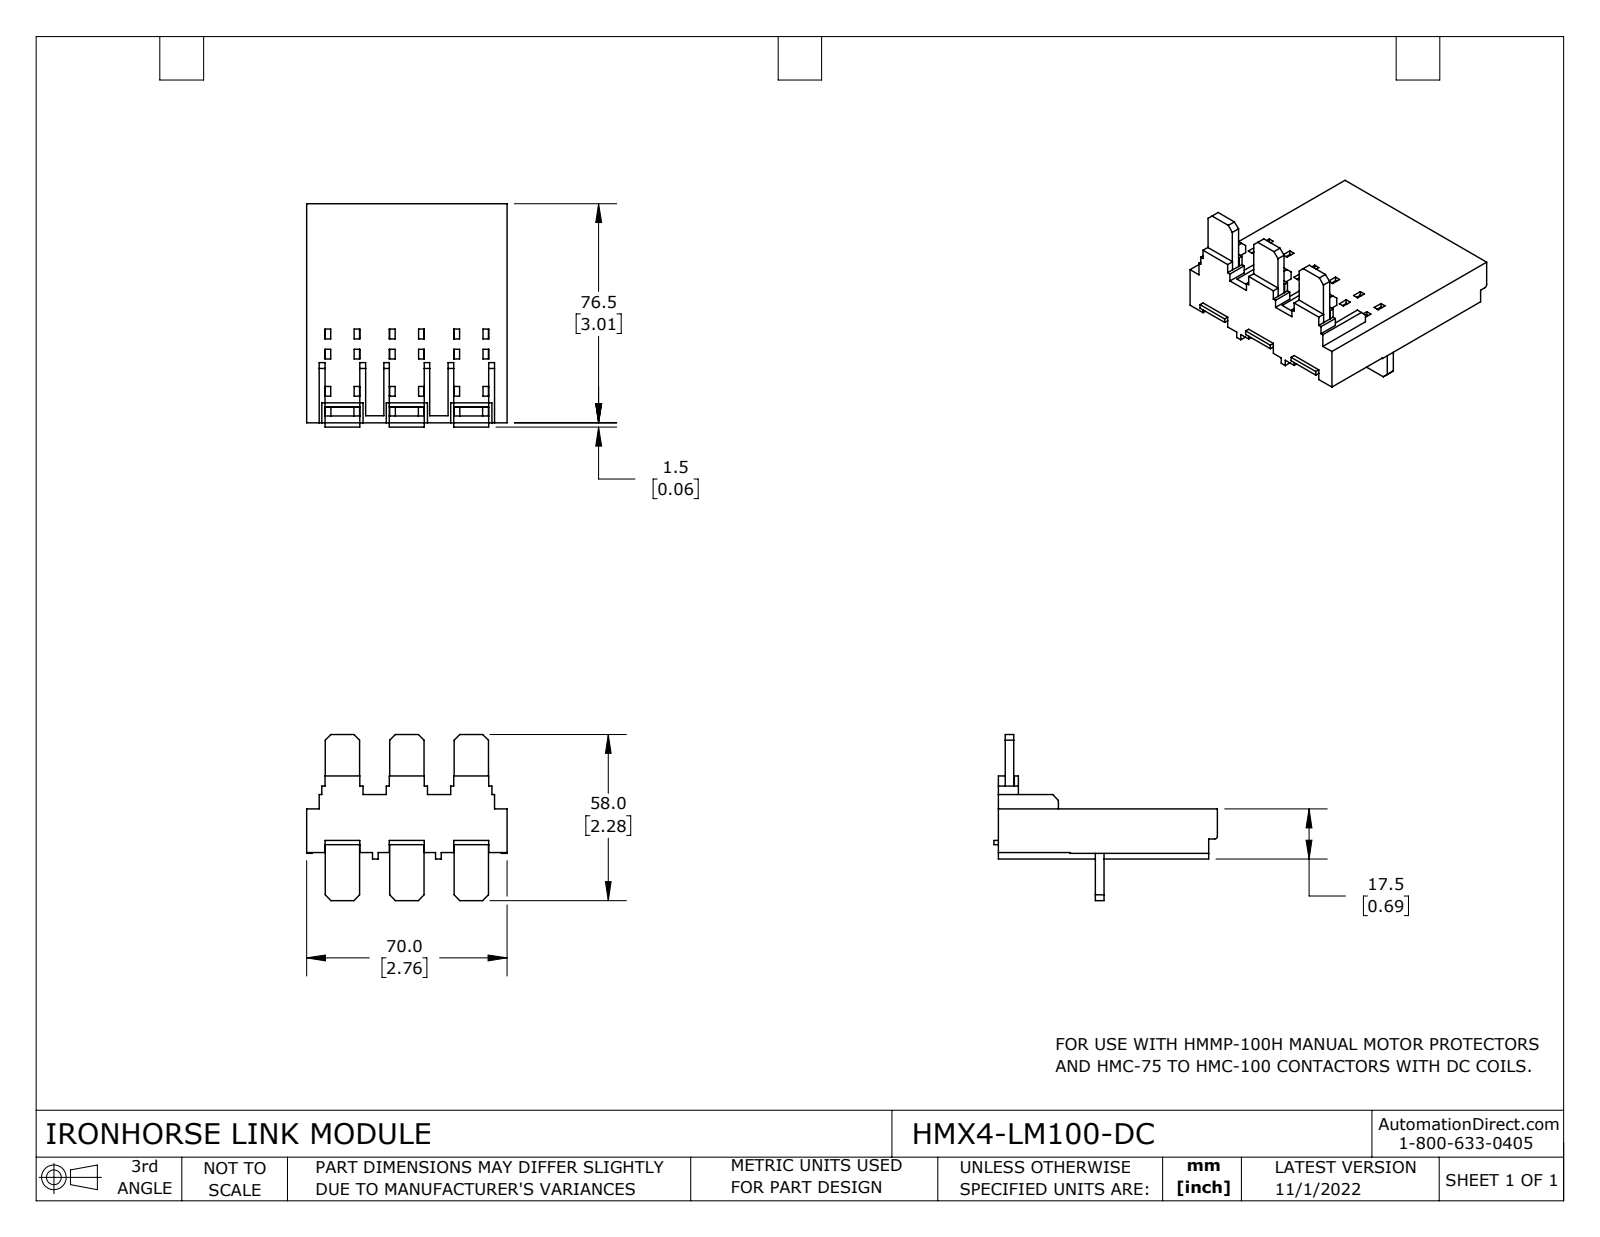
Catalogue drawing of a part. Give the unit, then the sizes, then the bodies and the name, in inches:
Units: inches
Overall size (bounding box): 3.071 × 2.756 × 2.283
Partial cylindrical surfaces — rounded edges, fillets, slot ends (radius × count): R0.02 ×6, R0.039 ×5, R0.157 ×2
Main face-to-face distances: 0.079, 1.772, 0.906, 0.118, 0.098, 0.984, 0.866, 1.85, 0.177, 0.886
Volume: 2.122 in³ · Surface area: 50.83 in²
Bodies: 1 solid, 650 faces (622 planar, 28 cylindrical, 0 other)
Part name (STEP PRODUCT): HMX4-LM100-DC
STEP written by: SolidWorks 2021 (CONFIG_CONTROL_DESIGN)
